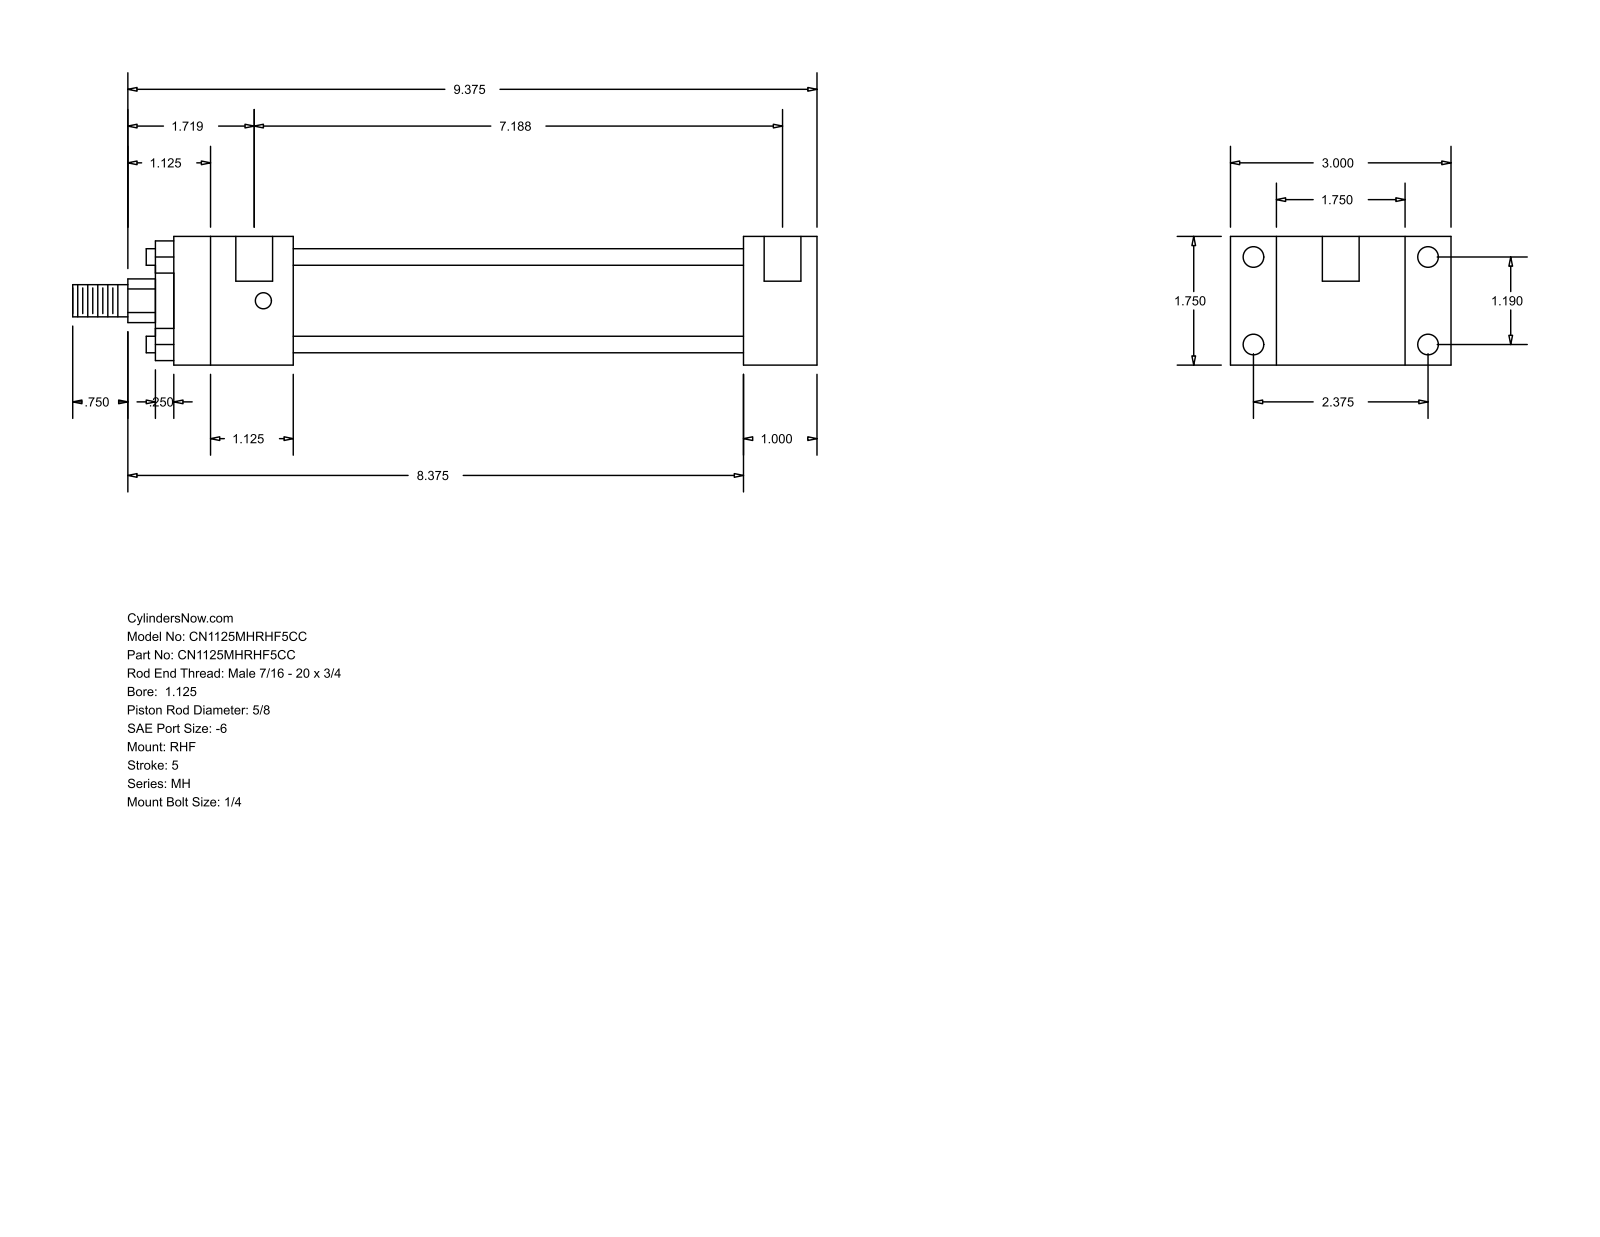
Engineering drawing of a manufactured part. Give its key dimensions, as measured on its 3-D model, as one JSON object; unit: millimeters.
{"part_name": "MH_RHF__0112_0.625", "step_written_by": "GSSL Pune (CONFIG_CONTROL_DESIGN)", "units": "millimeters", "bodies": {"solids": 0, "faces": 88, "planar": 60, "cylindrical": 28, "other": 0}, "overall_size": [257.18, 76.2, 44.45], "round_holes": [[5.56, 4], [7.14, 4], [12.7, 2]], "round_bosses_or_shafts": [[5.71, 4], [34.92, 1], [28.57, 1], [15.88, 1], [11.11, 1]], "partial_cylinders_radius": [[7.54, 1]], "face_to_face_distances": [44.46, 15.87, 25.4, 60.33, 76.2, 155.57, 180.97, 41.27, 196.84, 222.24], "hole_center_spacings": [30.22, 60.32, 67.47, 179.39, 3.17, 182.56]}
